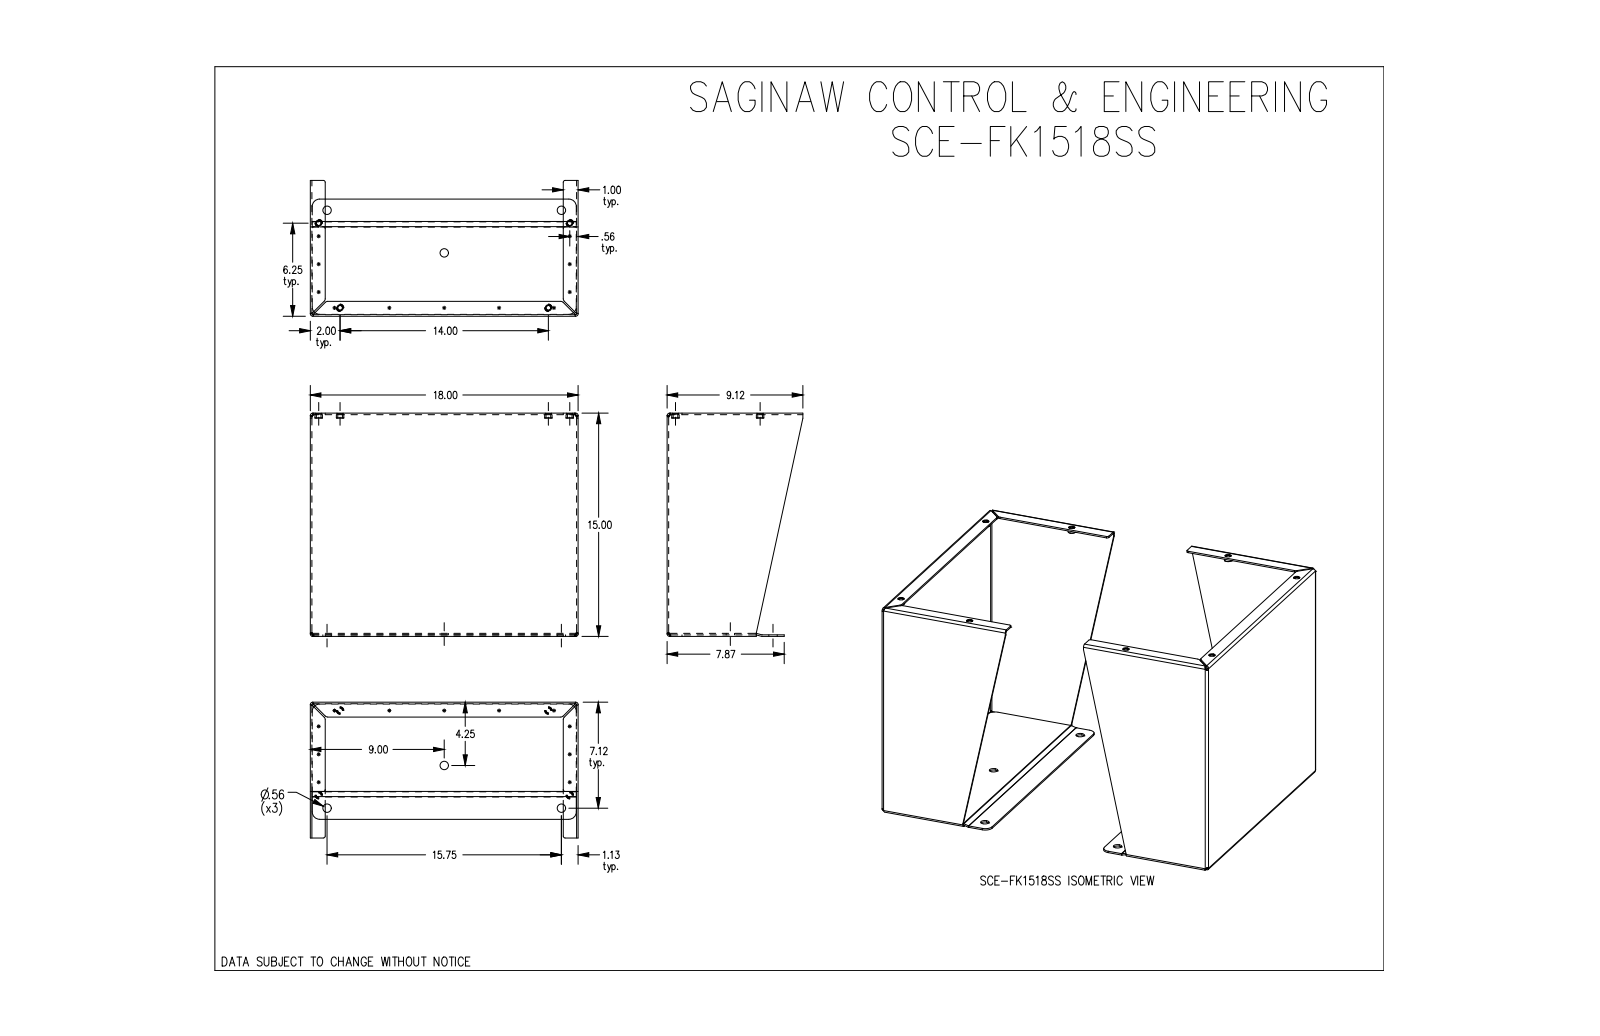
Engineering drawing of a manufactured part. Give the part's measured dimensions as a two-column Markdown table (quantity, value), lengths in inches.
| quantity | value |
| --- | --- |
| part name | SCE-FK1518SS |
| STEP written by | SolidWorks 2019 (CONFIG_CONTROL_DESIGN) |
| units | inches |
| bodies | 12 solids, 286 faces (120 planar, 110 cylindrical, 56 other) |
| overall size | 24 × 18 × 15 |
| volume | 141.7 in³ |
| surface area | 2 762 in² |
| round holes (diameter × count) | 0.312 × 8, 0.413 × 8, 0.563 × 6 |
| round bosses / shafts (diameter × count) | 0.5 × 8, 0.412 × 8 |
| partial cylindrical surfaces (radius × count) | 0.166 × 16, 0.062 × 12, 0.125 × 8, 0.22 × 8, 0.5 × 8, 0.063 × 6 |
| main face-to-face distances | 0.104, 23.896, 17.896, 24, 23.792, 18, 17.792, 14.792, 0.101, 14.893 |
| hole center spacings | 1.035, 5.866, 6.614, 7.913, 8.671, 10.646, 14.884, 15.919 |
